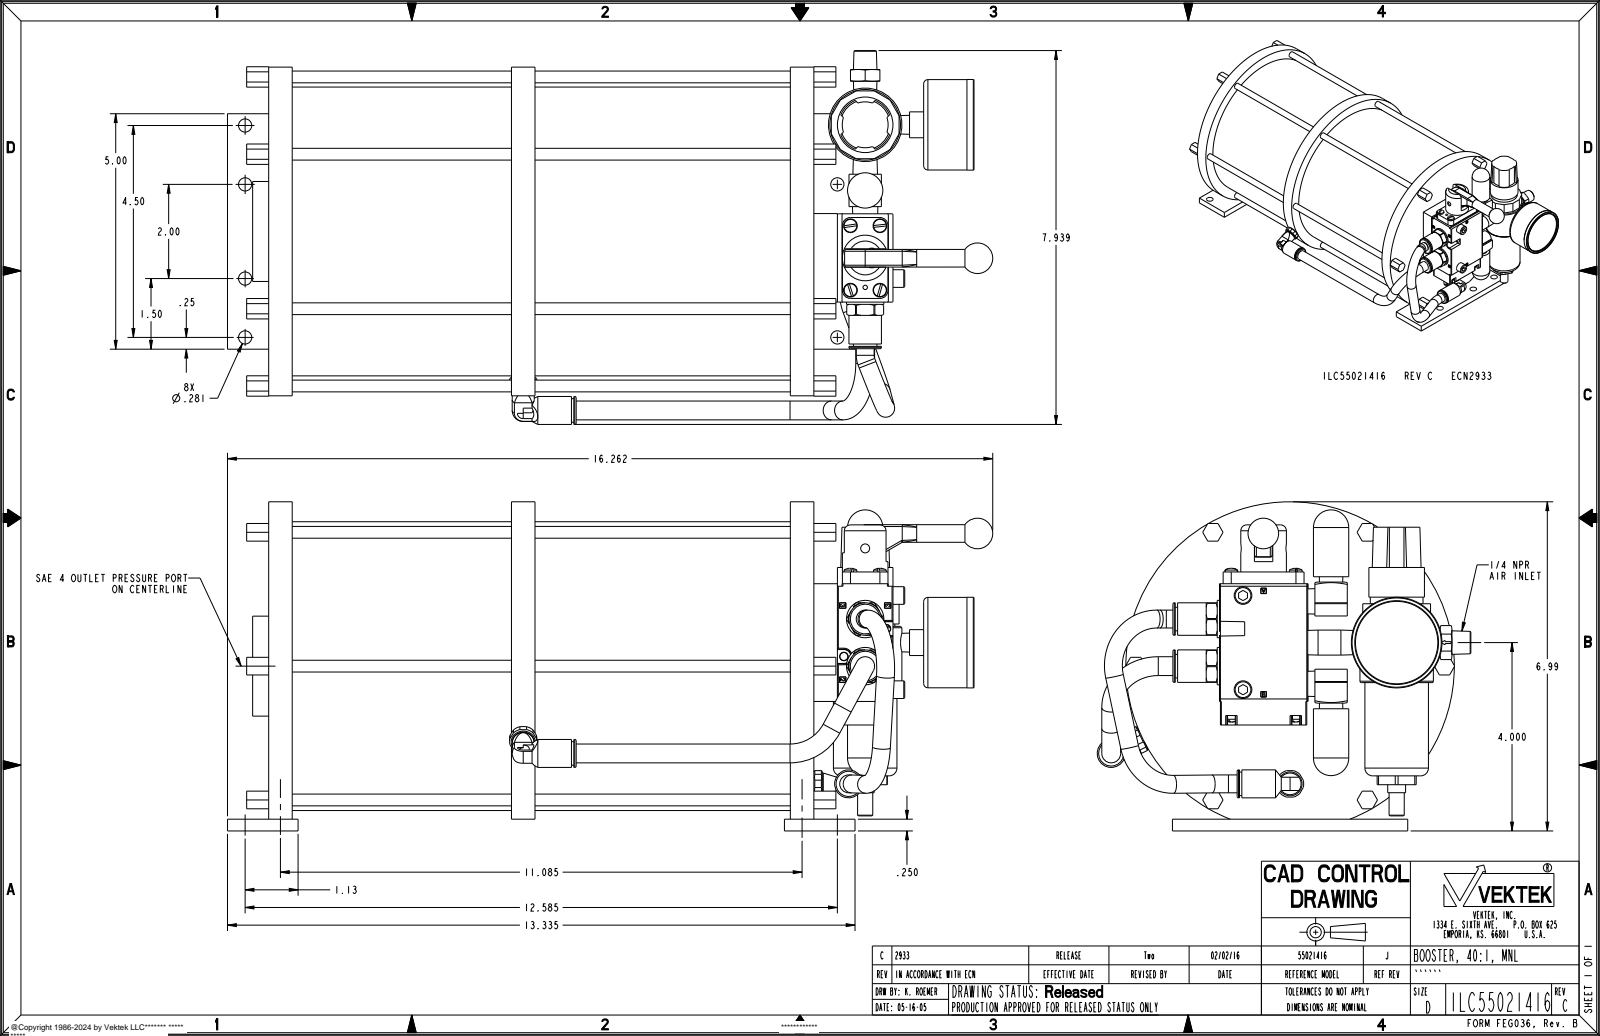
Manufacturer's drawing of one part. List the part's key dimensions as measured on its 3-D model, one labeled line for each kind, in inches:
Part name (STEP PRODUCT): ILC55021416
STEP written by: PRO/ENGINEER BY PARAMETRIC TECHNOLOGY CORPORATION, 2013320 (CONFIG_CONTROL_DESIGN)
Units: inches
Bodies: 1 solid, 1189 faces (552 planar, 330 cylindrical, 307 other)
Overall size (bounding box): 16.261 × 7.939 × 6.99
Volume: 365 in³ · Surface area: 583.8 in²
Round holes (diameter × count): ⌀0.281 ×12, ⌀0.201 ×4, ⌀0.5 ×3, ⌀0.213 ×2, ⌀0.262 ×2, ⌀0.375 ×2, ⌀0.54 ×2, ⌀0.69 ×2, ⌀0.794 ×2, ⌀0.094 ×1, ⌀0.098 ×1, ⌀0.145 ×1
Round bosses / shafts (diameter × count): ⌀0.25 ×12, ⌀0.38 ×6, ⌀0.4 ×4, ⌀0.375 ×4, ⌀0.272 ×4, ⌀0.46 ×3, ⌀0.594 ×2, ⌀0.5 ×2
Partial cylindrical surfaces — rounded edges, fillets, slot ends (radius × count): R0.039 ×19, R0.02 ×16, R0.06 ×6, R0.02 ×4, R0.13 ×4, R0.146 ×4, R0.172 ×4, R0.234 ×4
Main face-to-face distances: 11.585, 0.5, 11.085, 5.159, 5.926, 0.25, 6.426, 5.659, 4.659, 10.585
Hole centre spacings: 2, 0.75, 1.25, 1.458, 2.136, 3.25, 3.335, 11.835
